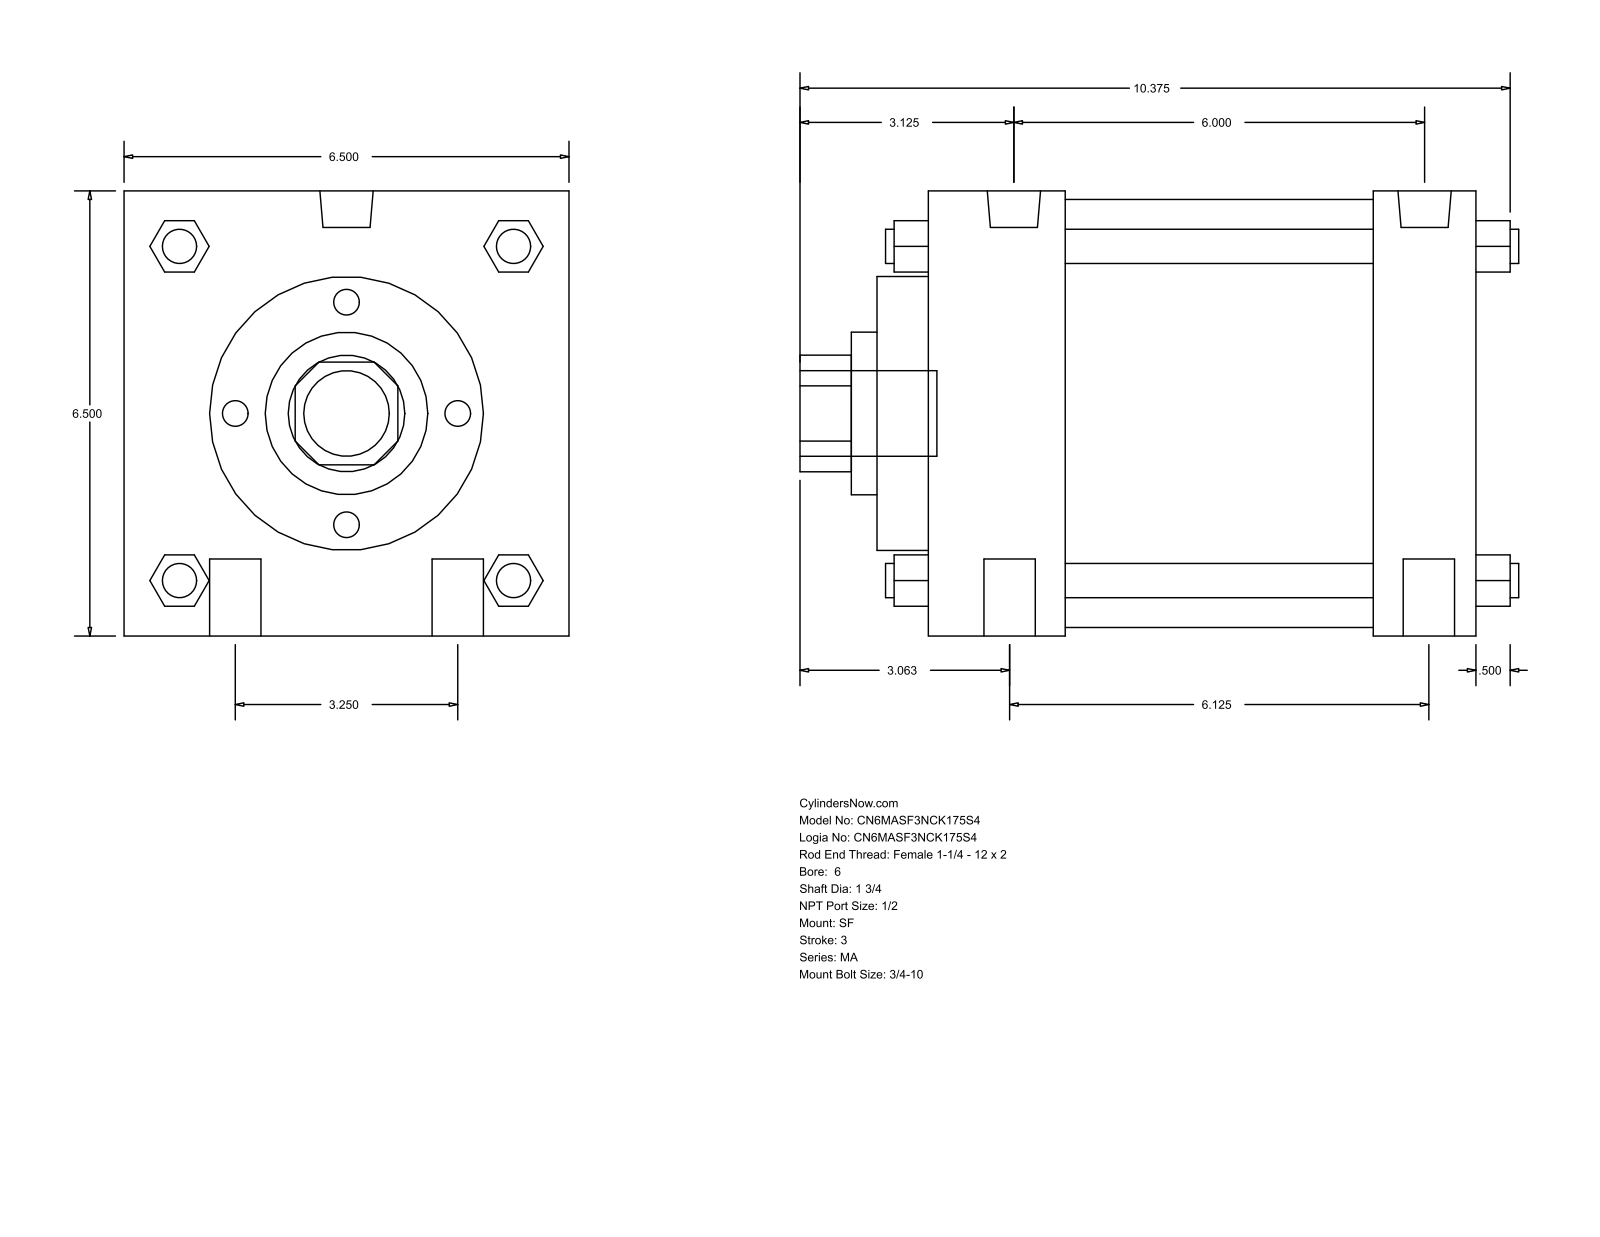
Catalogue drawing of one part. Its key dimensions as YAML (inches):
part_name: "MA_SF__0600_1.75"
step_written_by: "GSSL Pune (CONFIG_CONTROL_DESIGN)"
units: inches
bodies: {solids: 0, faces: 126, planar: 95, cylindrical: 31, other: 0}
overall_size: [10.5, 6.5, 6.5]
round_holes:
  - {diameter: 1.75, count: 1}
  - {diameter: 2.375, count: 1}
  - {diameter: 4, count: 1}
  - {diameter: 6.25, count: 1}
round_bosses_or_shafts:
  - {diameter: 0.75, count: 4}
  - {diameter: 0.5, count: 4}
  - {diameter: 0.778, count: 2}
  - {diameter: 0.687, count: 2}
  - {diameter: 1.25, count: 1}
partial_cylinders:
  - {radius: 0.852, count: 1}
face_to_face_distances: [6.5, 8, 0.75, 2, 6, 1.5, 4.5, 2.75, 7.25, 8.75]
